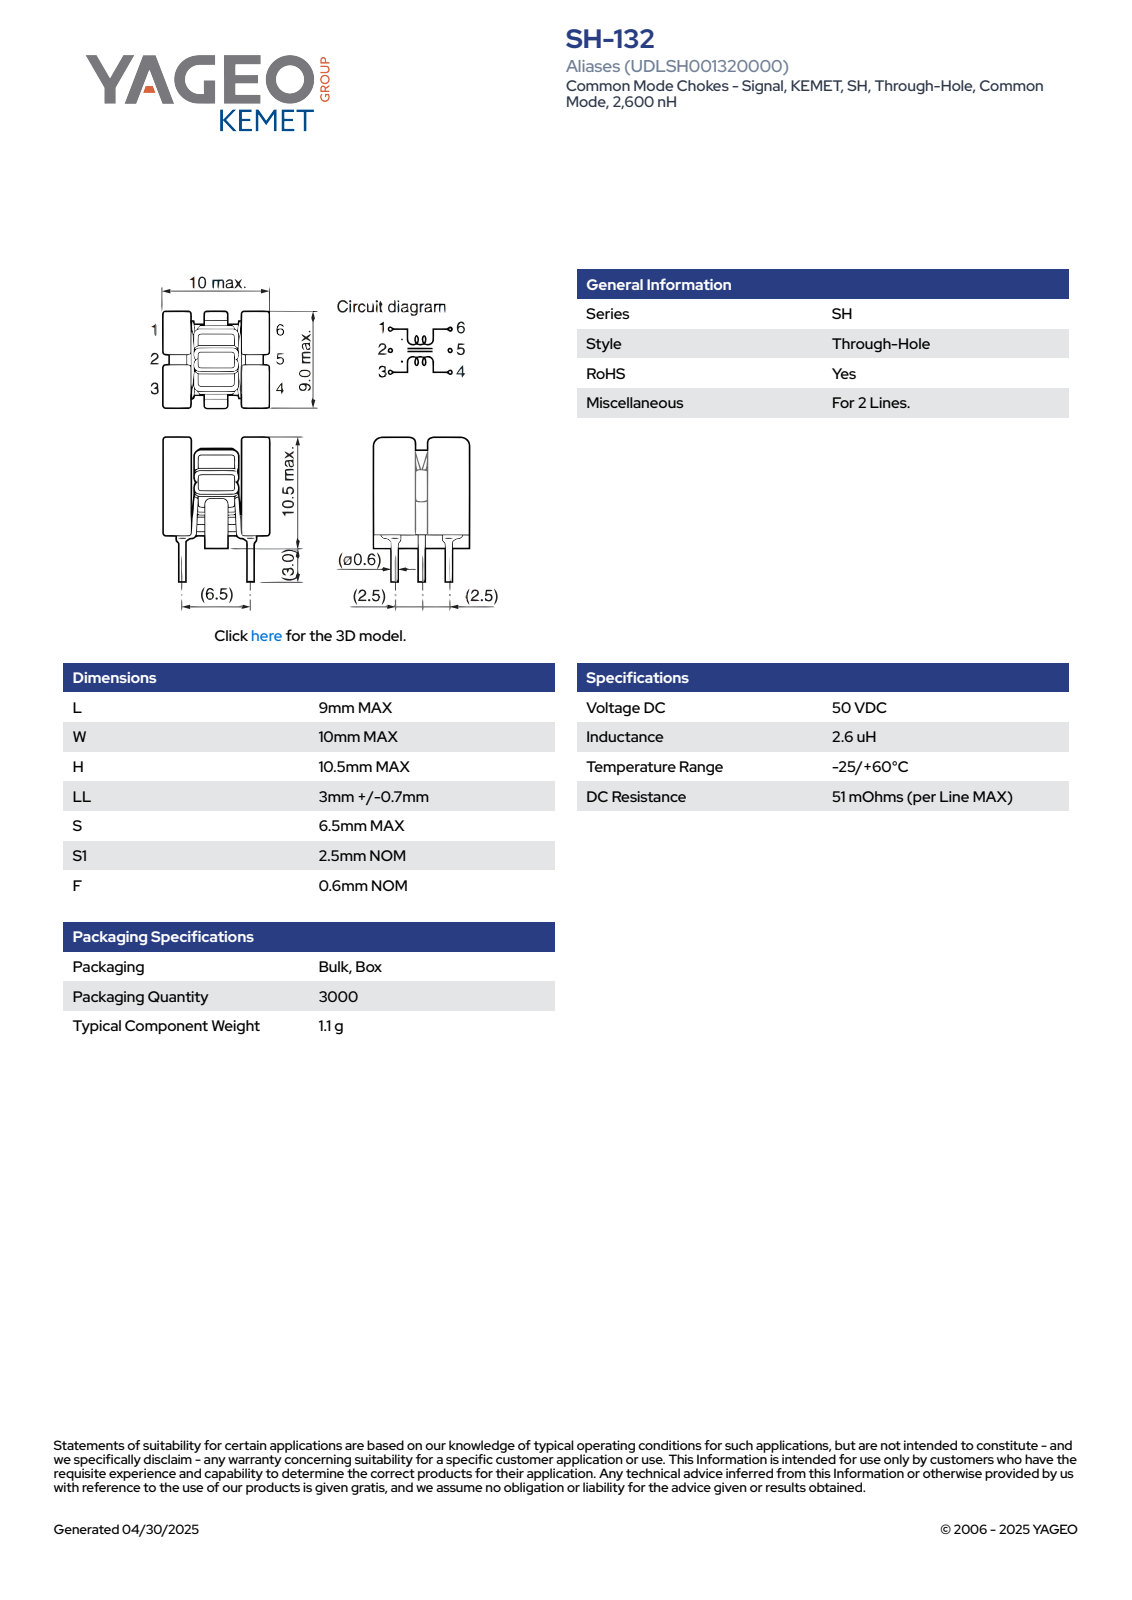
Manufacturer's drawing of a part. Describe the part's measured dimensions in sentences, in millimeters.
The part is named "IFC_DCSH4_L9W10H10.5". Its 3-D file was written by "SolidWorks 2014 (AUTOMOTIVE_DESIGN)". It is 13 solids with 498 faces: 124 planar, 254 cylindrical and 120 other. Overall it measures 13.51 by 10 by 9 millimeters. Its volume is 580 cubic millimeters and its surface area 958 square millimeters. Round holes: 1 of diameter 2.13. Round bosses or shafts: 36 of diameter 0.25, 6 of diameter 0.6, 1 of diameter 5.75. Partial cylindrical surfaces (rounded edges, fillets, slot ends): 38 of radius 0.25, 5 of radius 0.12. The main face-to-face distances are 2.1, 7.9, 3, 3.98, 5.02, 10, 5.8, 9, 4.9, 7.
